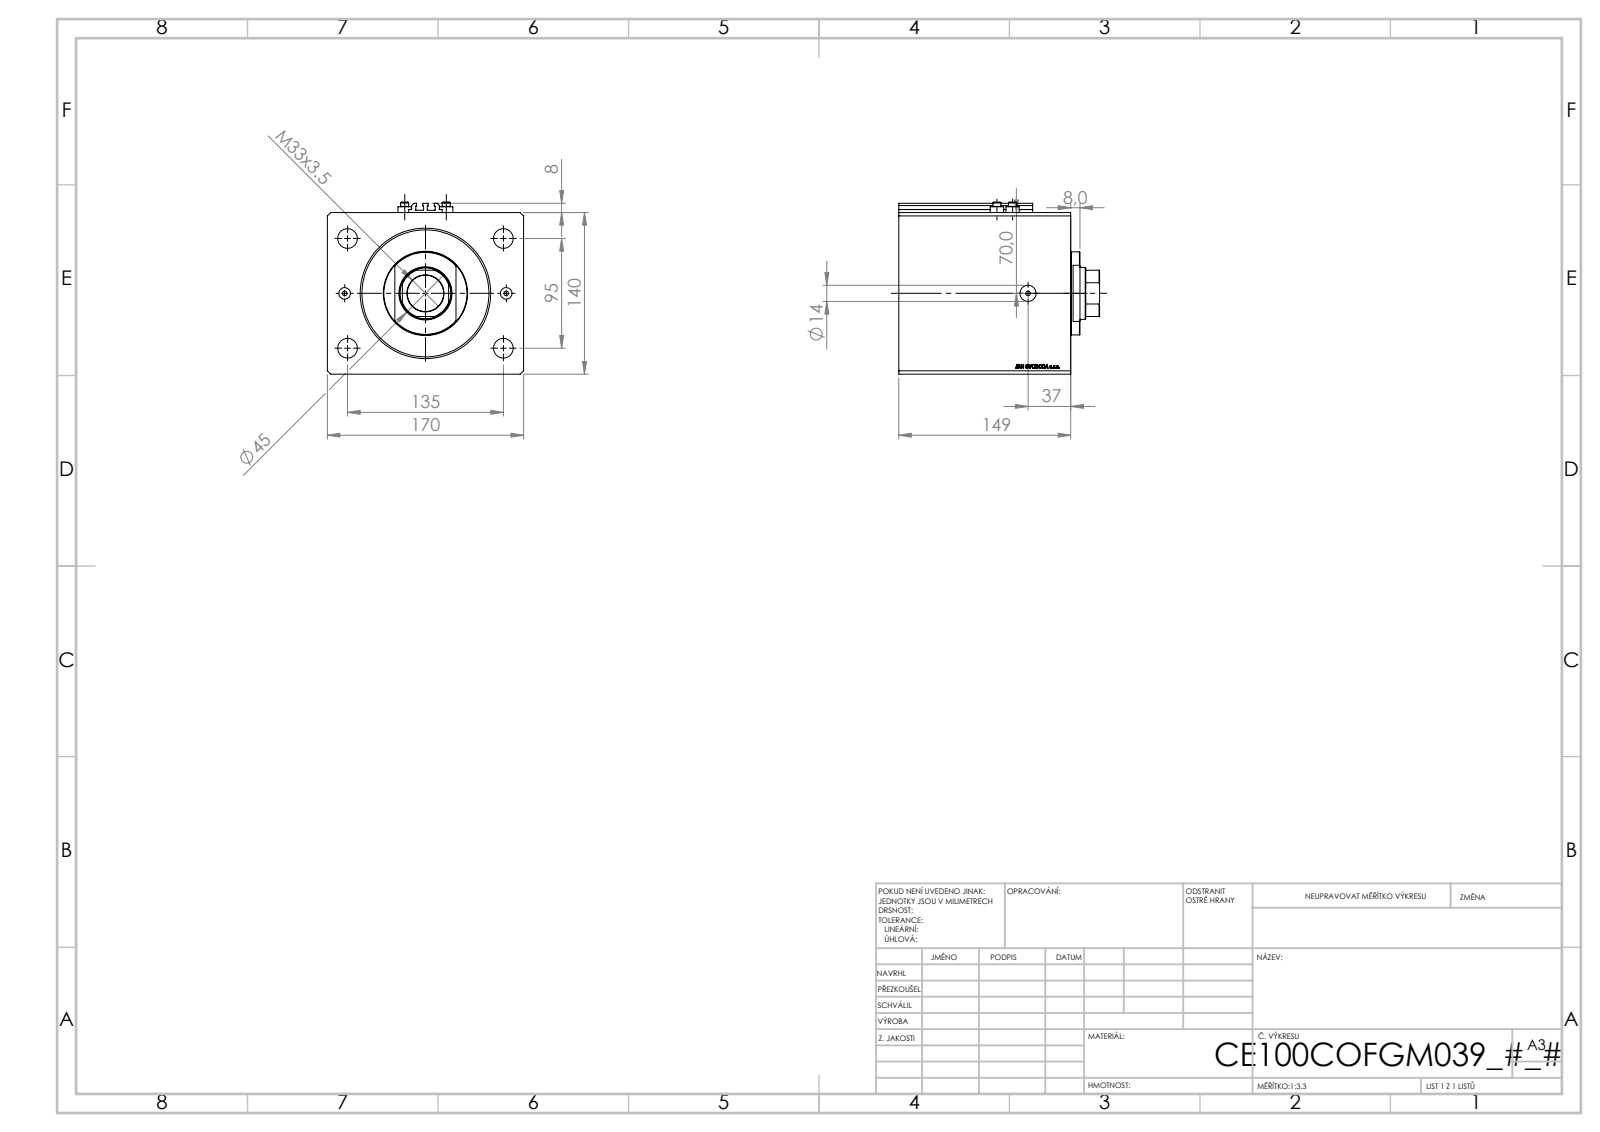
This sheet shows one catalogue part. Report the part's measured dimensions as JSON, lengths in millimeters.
{"part_name": "V250CE_VC_C; ALLEN BOLT V250CE; V250CE_C_Body; V250CE_C_VCP", "step_written_by": "SolidWorks 2019 (CONFIG_CONTROL_DESIGN)", "units": "millimeters", "bodies": {"solids": 8, "faces": 1034, "planar": 504, "cylindrical": 86, "other": 444}, "overall_size": [174, 170, 149], "volume_mm3": 3186000, "surface_area_mm2": 307359, "round_holes": [[4, 8], [17, 4], [10, 2], [14, 2], [31.5, 1], [45, 1], [100, 1], [113, 1]], "round_bosses_or_shafts": [[11.6, 4], [7, 4], [72, 1]], "partial_cylinders_radius": [[0.2, 10], [22, 1]], "face_to_face_distances": [140, 170, 149, 28.9, 120.1, 25, 124, 95.1, 85, 56.1], "hole_center_spacings": [47.57, 82.54, 145.47, 13.6, 36, 38.48, 70, 95]}
